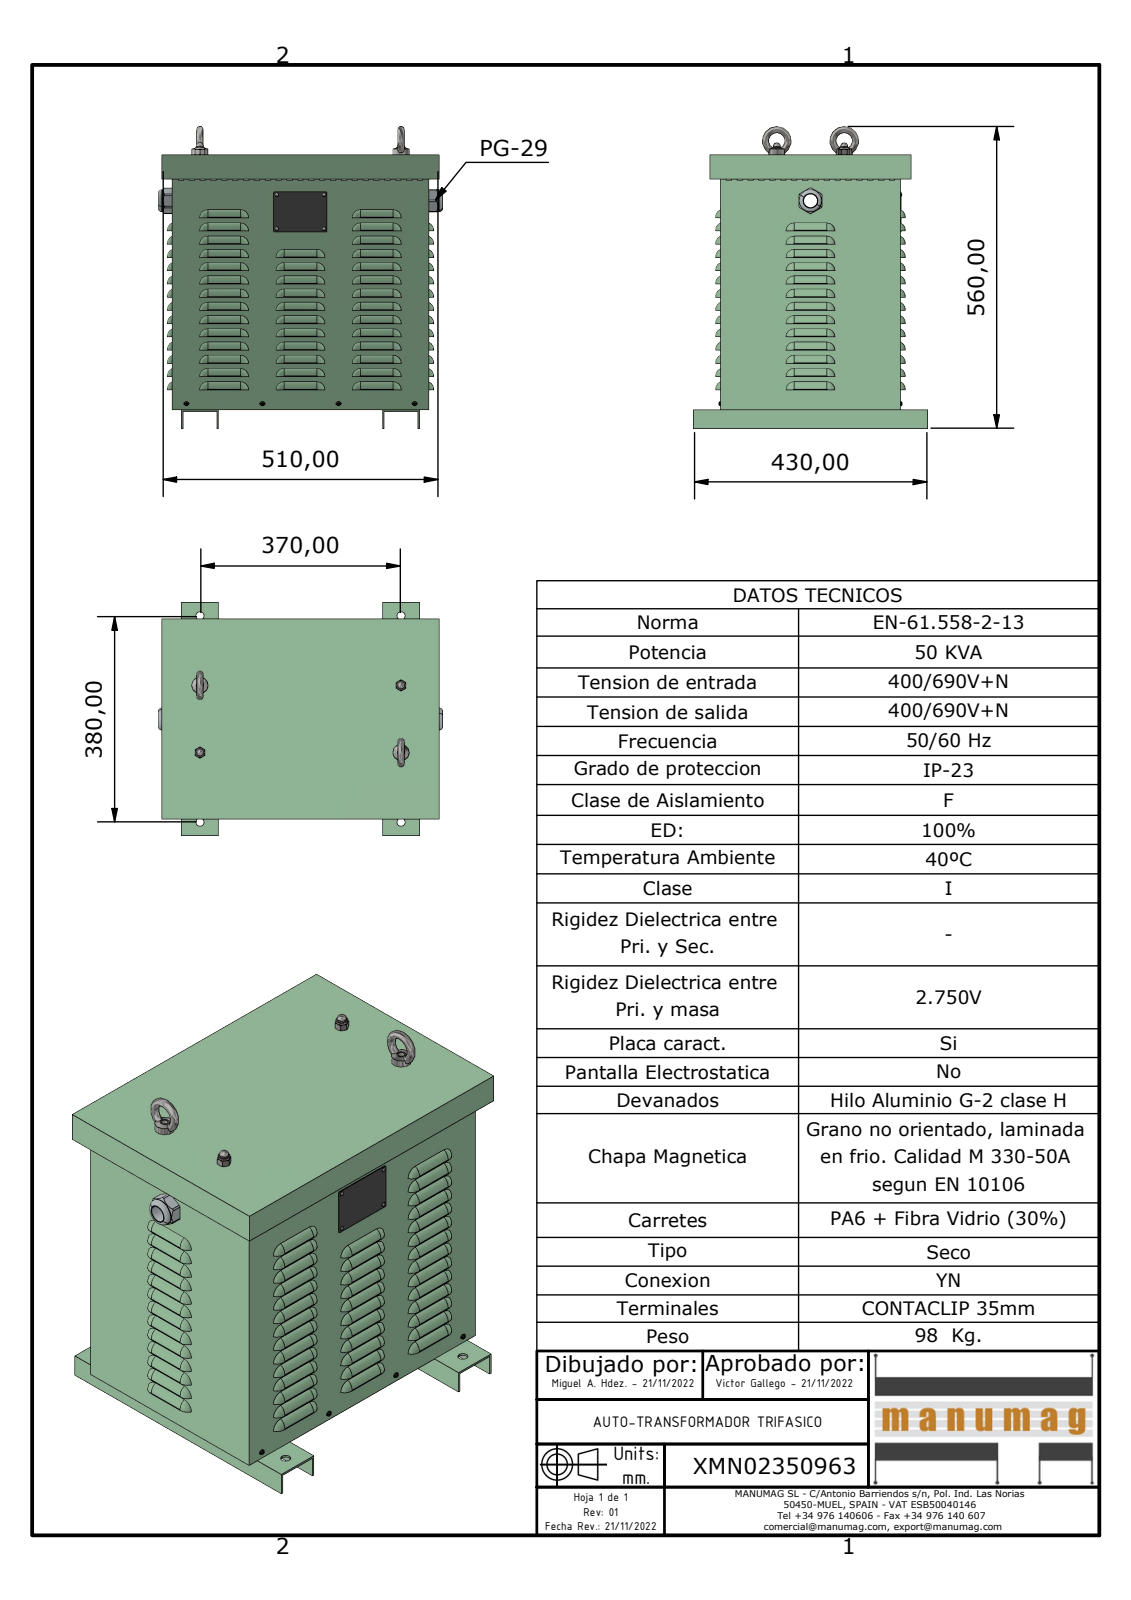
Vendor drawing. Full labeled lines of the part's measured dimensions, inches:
Part name (STEP PRODUCT): XMN02350963; JE040 - JE050 CUERPO; JE040 - JE050 BASE; JE040 - JE050 PATAS (+7 more)
STEP written by: Autodesk Inventor 2023 (AUTOMOTIVE_DESIGN)
Units: inches
Bodies: 24 solids, 2403 faces (969 planar, 808 cylindrical, 626 other)
Overall size (bounding box): 22.047 × 20.606 × 16.969
Volume: 190.1 in³ · Surface area: 4 290 in²
Round holes (diameter × count): ⌀0.433 ×260, ⌀0.157 ×4, ⌀0.197 ×4, ⌀0.398 ×4, ⌀0.551 ×4, ⌀0.591 ×4, ⌀0.984 ×1, ⌀1.496 ×1
Round bosses / shafts (diameter × count): ⌀0.157 ×4, ⌀0.143 ×4, ⌀0.126 ×4, ⌀1.181 ×2, ⌀0.709 ×2, ⌀0.535 ×2, ⌀1.606 ×1, ⌀1.469 ×1
Partial cylindrical surfaces — rounded edges, fillets, slot ends (radius × count): R0.551 ×104, R0.276 ×54, R0.591 ×54, R0.127 ×12, R0.098 ×8, R0.295 ×8, R0.079 ×4, R0.939 ×1
Main face-to-face distances: 0.079, 18.504, 18.583, 12.953, 18.425, 12.874, 13.031, 0.118, 0.768, 13.72
Hole centre spacings: 1.25, 2.819, 0.591, 1.102, 2.756, 1.756, 3.903, 5.543
